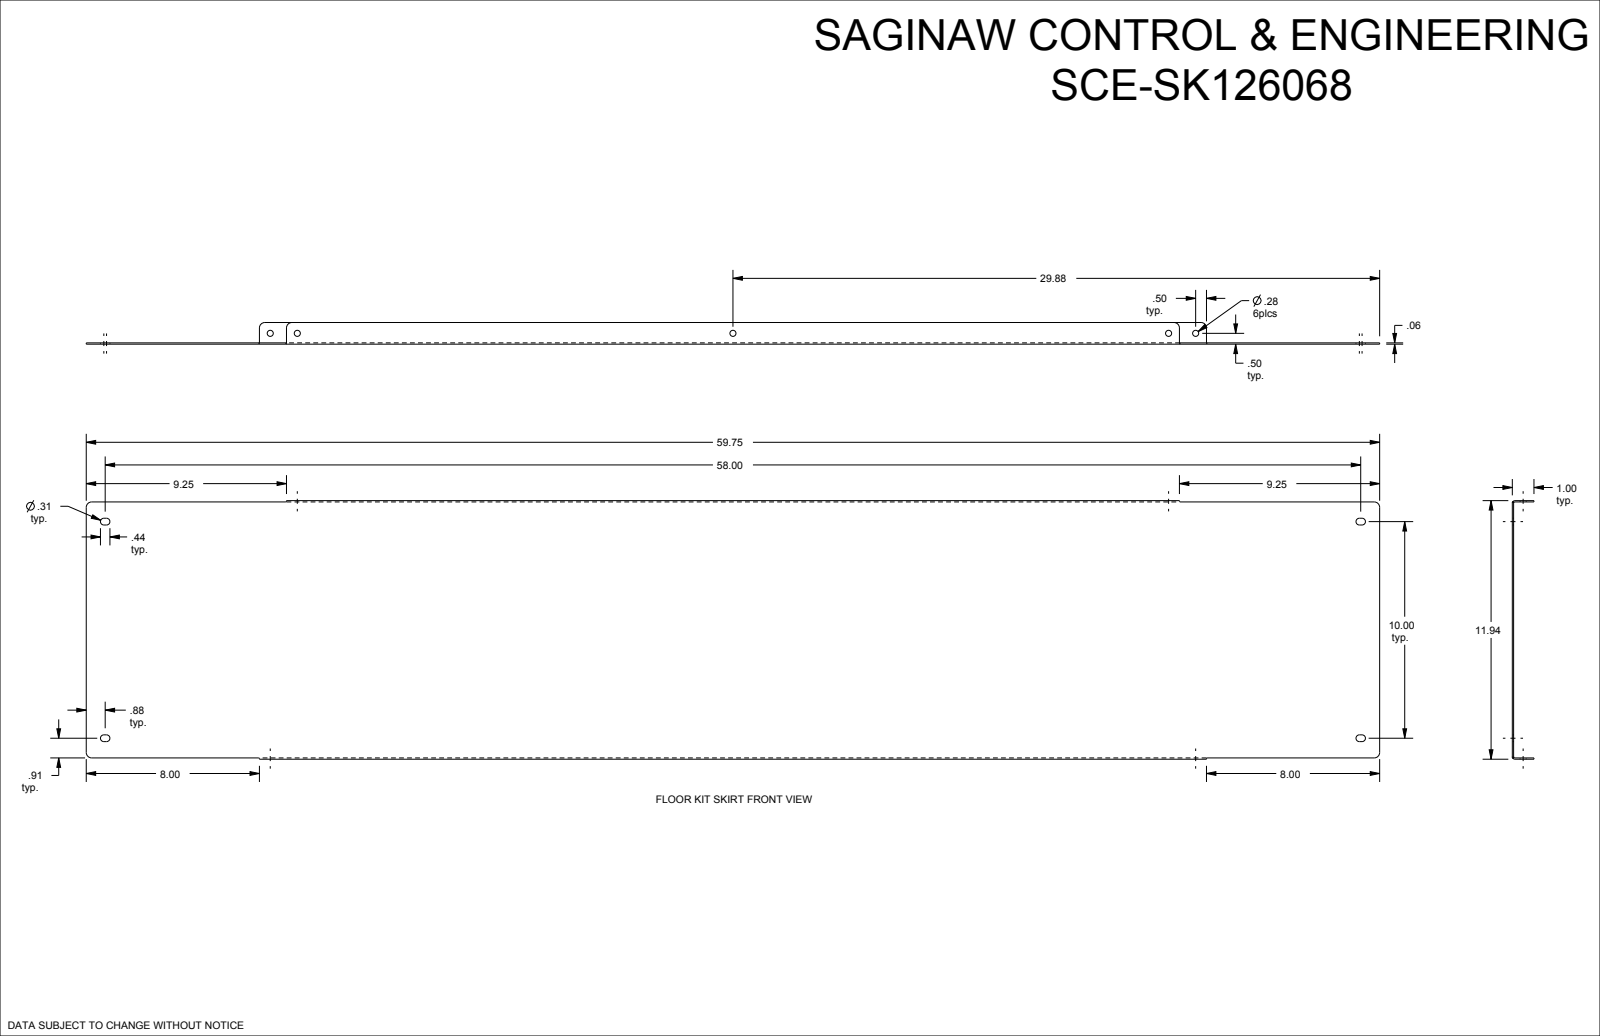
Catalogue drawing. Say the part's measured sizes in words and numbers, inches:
The part is named "SCE-SK126068". Its 3-D file was written by "SolidWorks 2021 (AUTOMOTIVE_DESIGN)". It is 1 solid with 64 faces: 26 planar, 26 cylindrical and 12 other. Overall it measures 59.75 by 11.938 by 1 inches. Its volume is 47.21 cubic inches and its surface area 1 583 square inches. Round holes: 5 of diameter 0.281. Partial cylindrical surfaces (rounded edges, fillets, slot ends): 8 of radius 0.156, 8 of radius 0.25, 2 of radius 0.06, 2 of radius 0.12. The main face-to-face distances are 0.06, 0.06, 11.878, 11.817, 11.938, 0.94, 1, 59.75, 9.25, 50.5. The hole center spacings are 1.25, 20.125, 21.375, 41.5, 40.25, 42.75.
